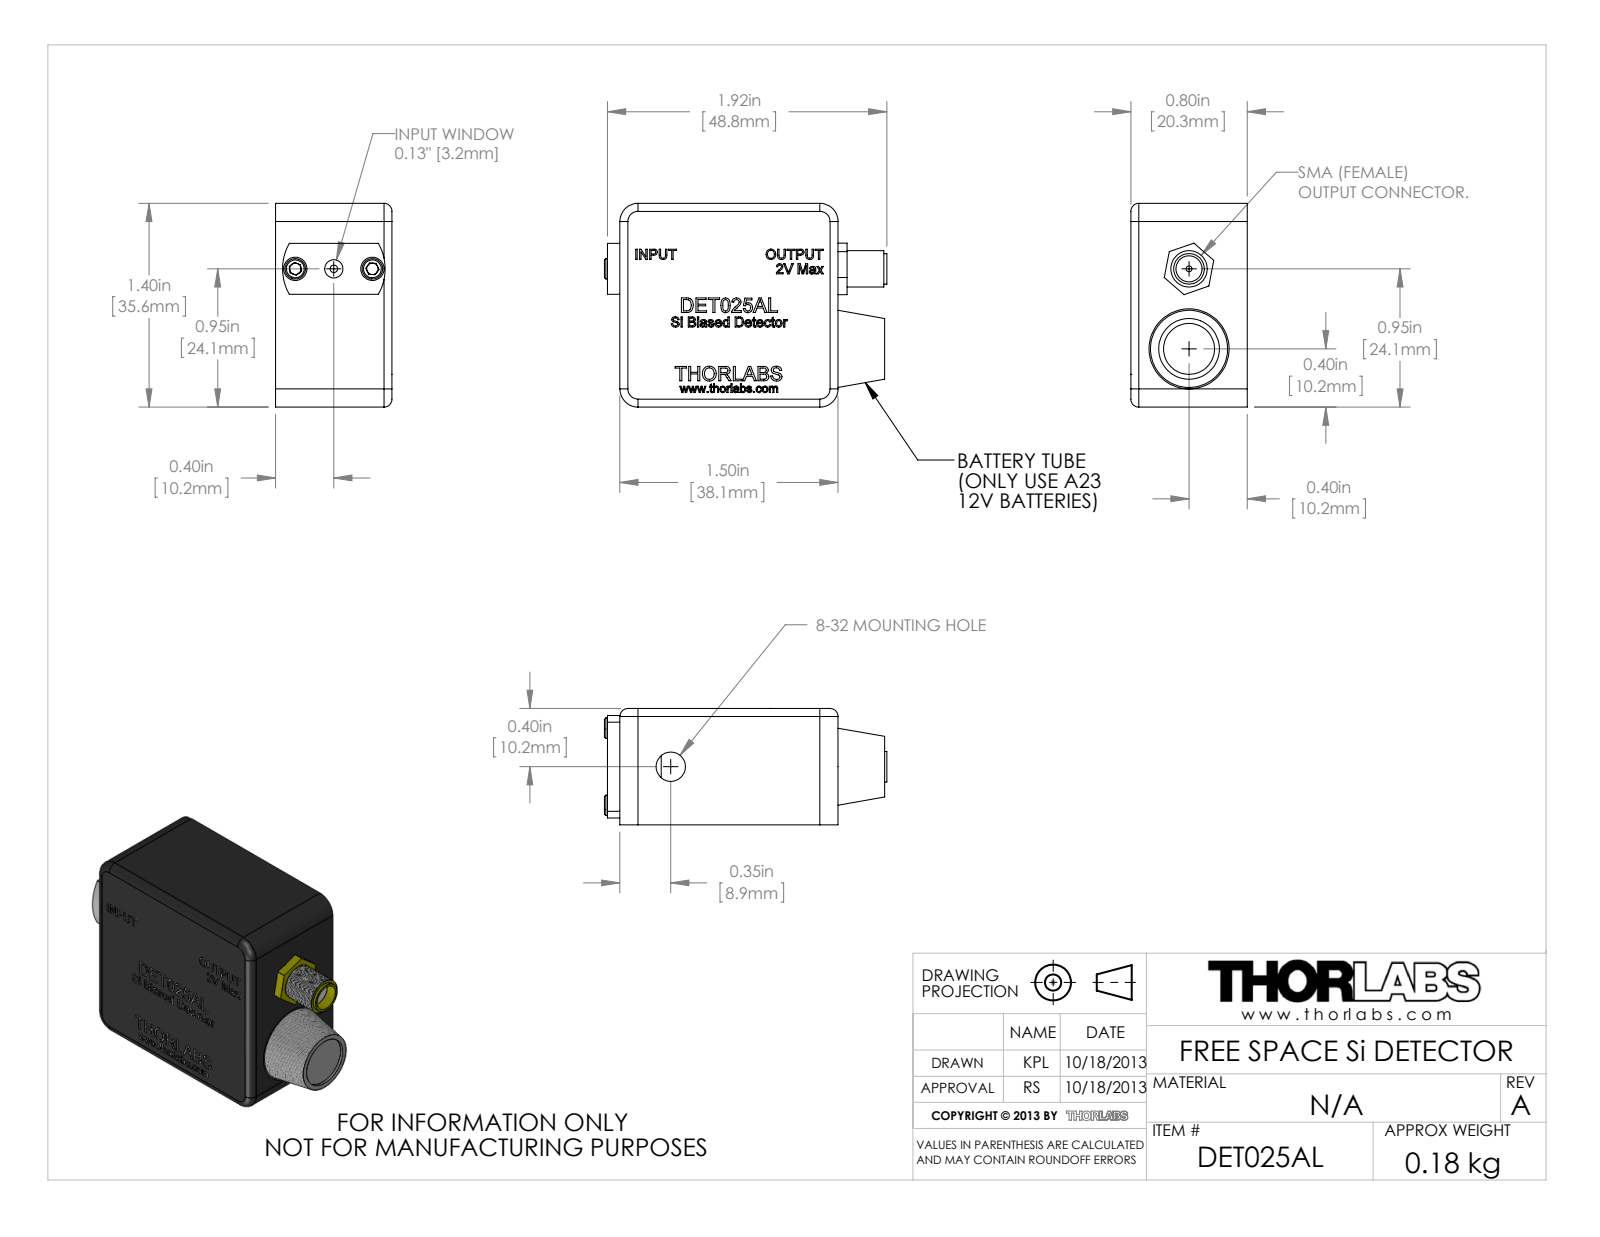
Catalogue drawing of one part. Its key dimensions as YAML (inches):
part_name: "TTN020155; Nut; flat head 100 screw_ai_CR-FHM1 0.086-64x0.188x0.188-N; socket head cap screw_ai_HX-SHCS 0.086-56x0.188x0.188-N (+6 more)"
step_written_by: "SolidWorks 2012 (AUTOMOTIVE_DESIGN)"
units: inches
bodies: {solids: 13, faces: 1645, planar: 977, cylindrical: 175, other: 493}
overall_size: [1.941, 1.4, 0.8]
volume: 1.181
surface_area: 22.75
round_holes:
  - {diameter: 0.07, count: 6}
  - {diameter: 0.096, count: 4}
  - {diameter: 0.125, count: 4}
  - {diameter: 0.14, count: 4}
  - {diameter: 0.085, count: 2}
  - {diameter: 0.16, count: 2}
  - {diameter: 0.017, count: 1}
  - {diameter: 0.04, count: 1}
  - {diameter: 0.05, count: 1}
  - {diameter: 0.125, count: 1}
  - {diameter: 0.179, count: 1}
  - {diameter: 0.186, count: 1}
round_bosses_or_shafts:
  - {diameter: 0.086, count: 6}
  - {diameter: 0.143, count: 4}
  - {diameter: 0.14, count: 2}
  - {diameter: 0.472, count: 1}
  - {diameter: 0.432, count: 1}
  - {diameter: 0.394, count: 1}
  - {diameter: 0.327, count: 1}
  - {diameter: 0.31, count: 1}
partial_cylinders:
  - {radius: 0.125, count: 12}
  - {radius: 0.032, count: 4}
  - {radius: 0.055, count: 4}
  - {radius: 0.08, count: 4}
  - {radius: 0.095, count: 4}
  - {radius: 0.06, count: 2}
  - {radius: 0.1, count: 2}
  - {radius: 0.008, count: 1}
face_to_face_distances: [0.063, 0.737, 0.8, 1.4, 0.5, 0.563, 0.237, 0.1, 1.5, 1.3]
hole_center_spacings: [1.698, 1.15, 1.15, 1.25, 1.25, 0.265, 0.611, 0.872]
